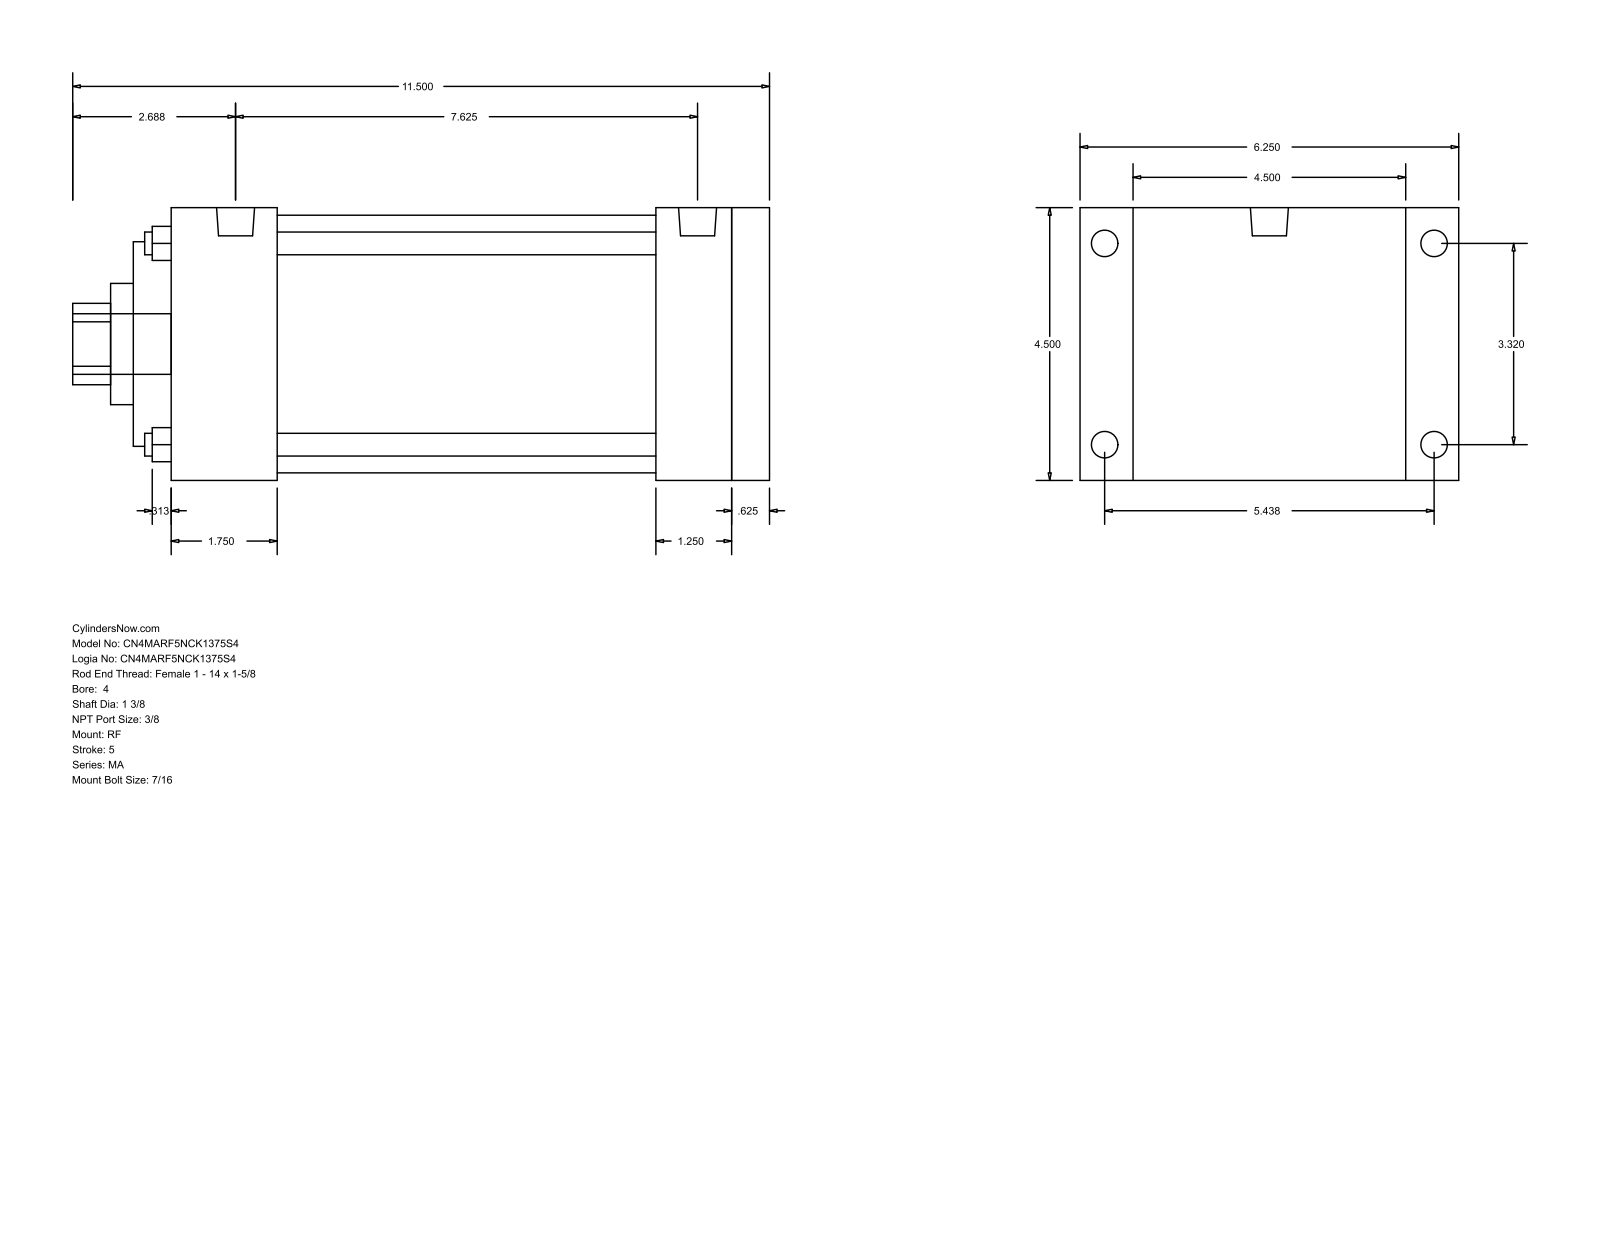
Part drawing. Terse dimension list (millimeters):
name: MA_RF__0400_1.375
written by: GSSL Pune (CONFIG_CONTROL_DESIGN)
unit: mm
bodies: 0 solids, 94 faces (65 planar, 29 cylindrical, 0 other)
size: 292.1 × 158.75 × 114.3
holes: 4× ⌀9.53, 1× ⌀34.92, 1× ⌀50.8, 1× ⌀85.72, 1× ⌀107.95
bosses: 8× ⌀11.11, 2× ⌀15.93, 1× ⌀25.4
rounds: 1× R17.06
face distances: 114.3, 250.83, 15.87, 234.96, 266.7, 22.23, 136.53, 219.07, 203.2, 31.76
hole spacings: 59.62, 84.32, 119.25
